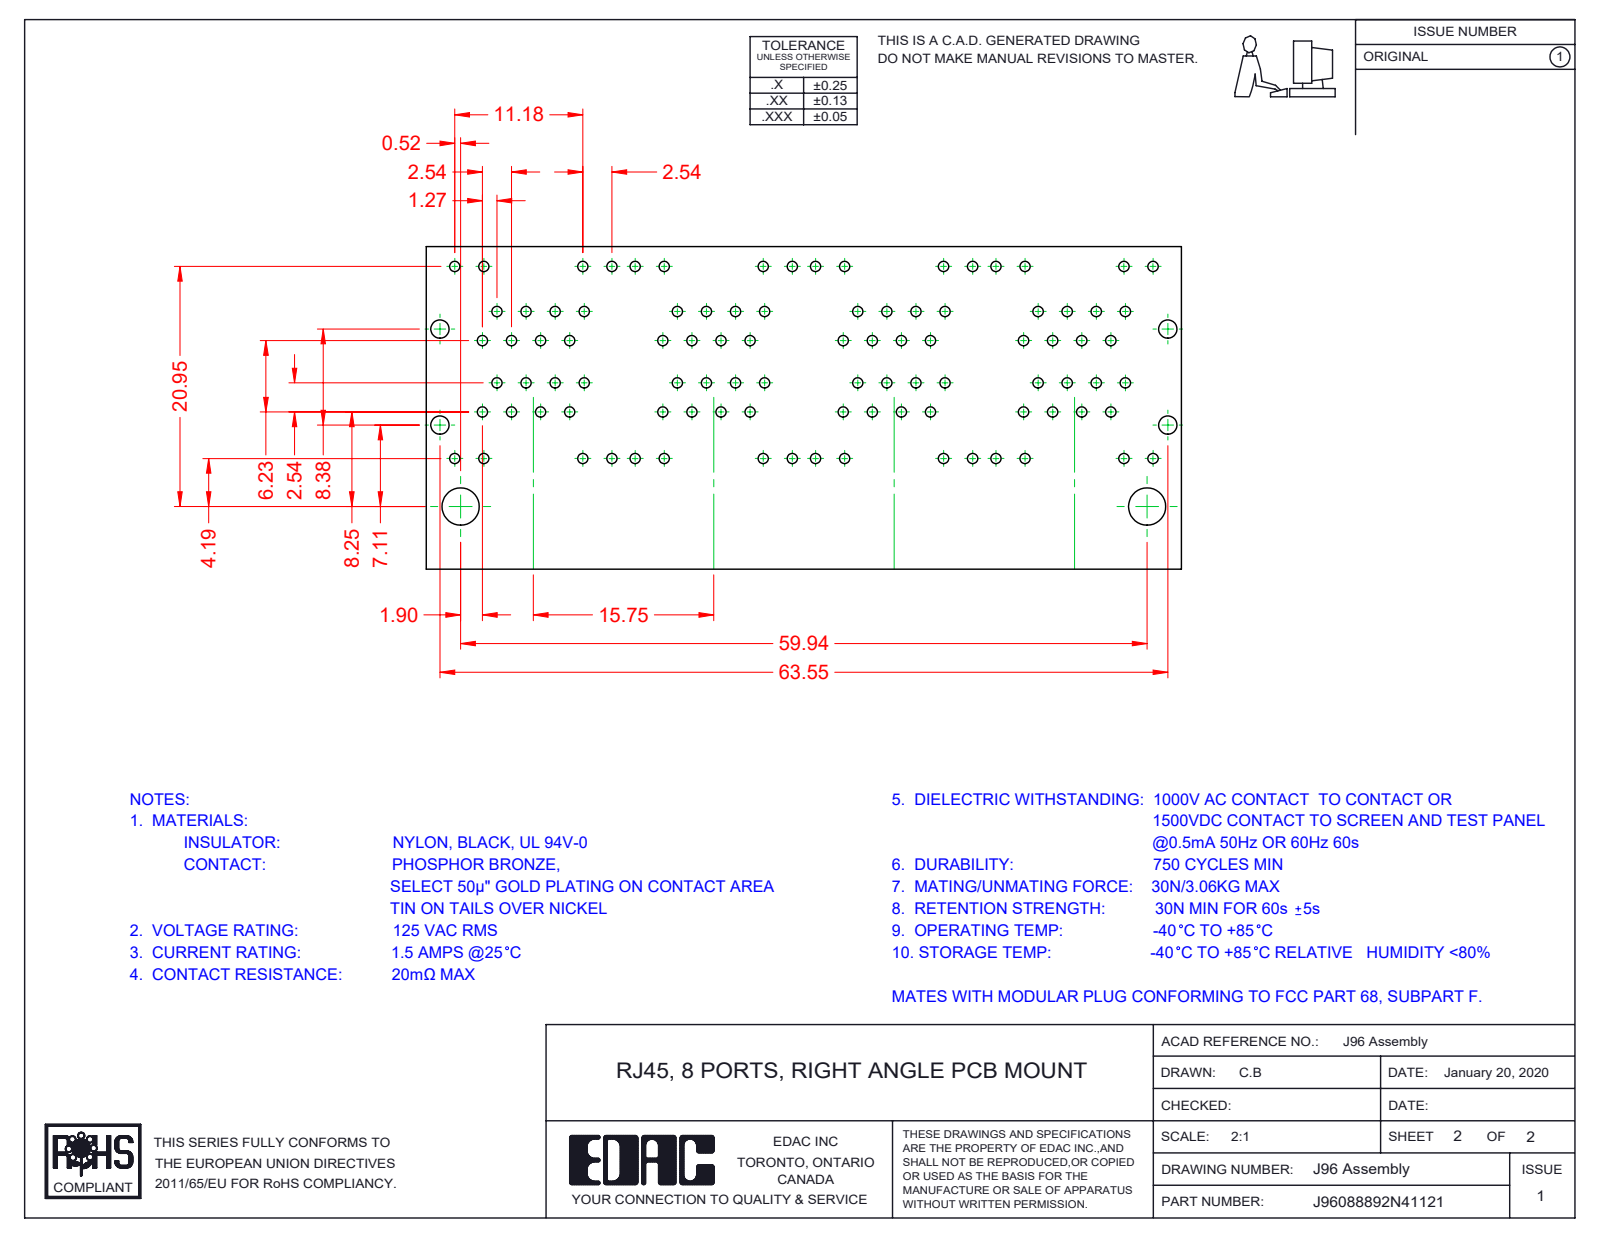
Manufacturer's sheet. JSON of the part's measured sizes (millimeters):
{"part_name": "96 Contact Lock Upper; 96 Back Plate_8 Ports; 96 Contacts Upper; 96 LED RH Lower_1-Yellow (+8 more)", "step_written_by": "SolidWorks 2016 (CONFIG_CONTROL_DESIGN)", "units": "millimeters", "bodies": {"solids": 96, "faces": 7642, "planar": 6069, "cylindrical": 1307, "other": 266}, "overall_size": [64.05, 29.58, 28.68], "volume_mm3": 24160, "surface_area_mm2": 63658, "round_holes": [[1.7, 3]], "round_bosses_or_shafts": [[1.68, 3]], "partial_cylinders_radius": [[0.25, 124], [0.35, 73], [1, 72], [0.5, 49], [0.91, 32], [0.2, 21], [0.7, 11], [0.22, 8]], "face_to_face_distances": [15.75, 0.35, 9.95, 1.17, 1.6, 0.54, 9.98, 10.18, 12.67, 3.37], "hole_center_spacings": [15.75, 31.5]}
